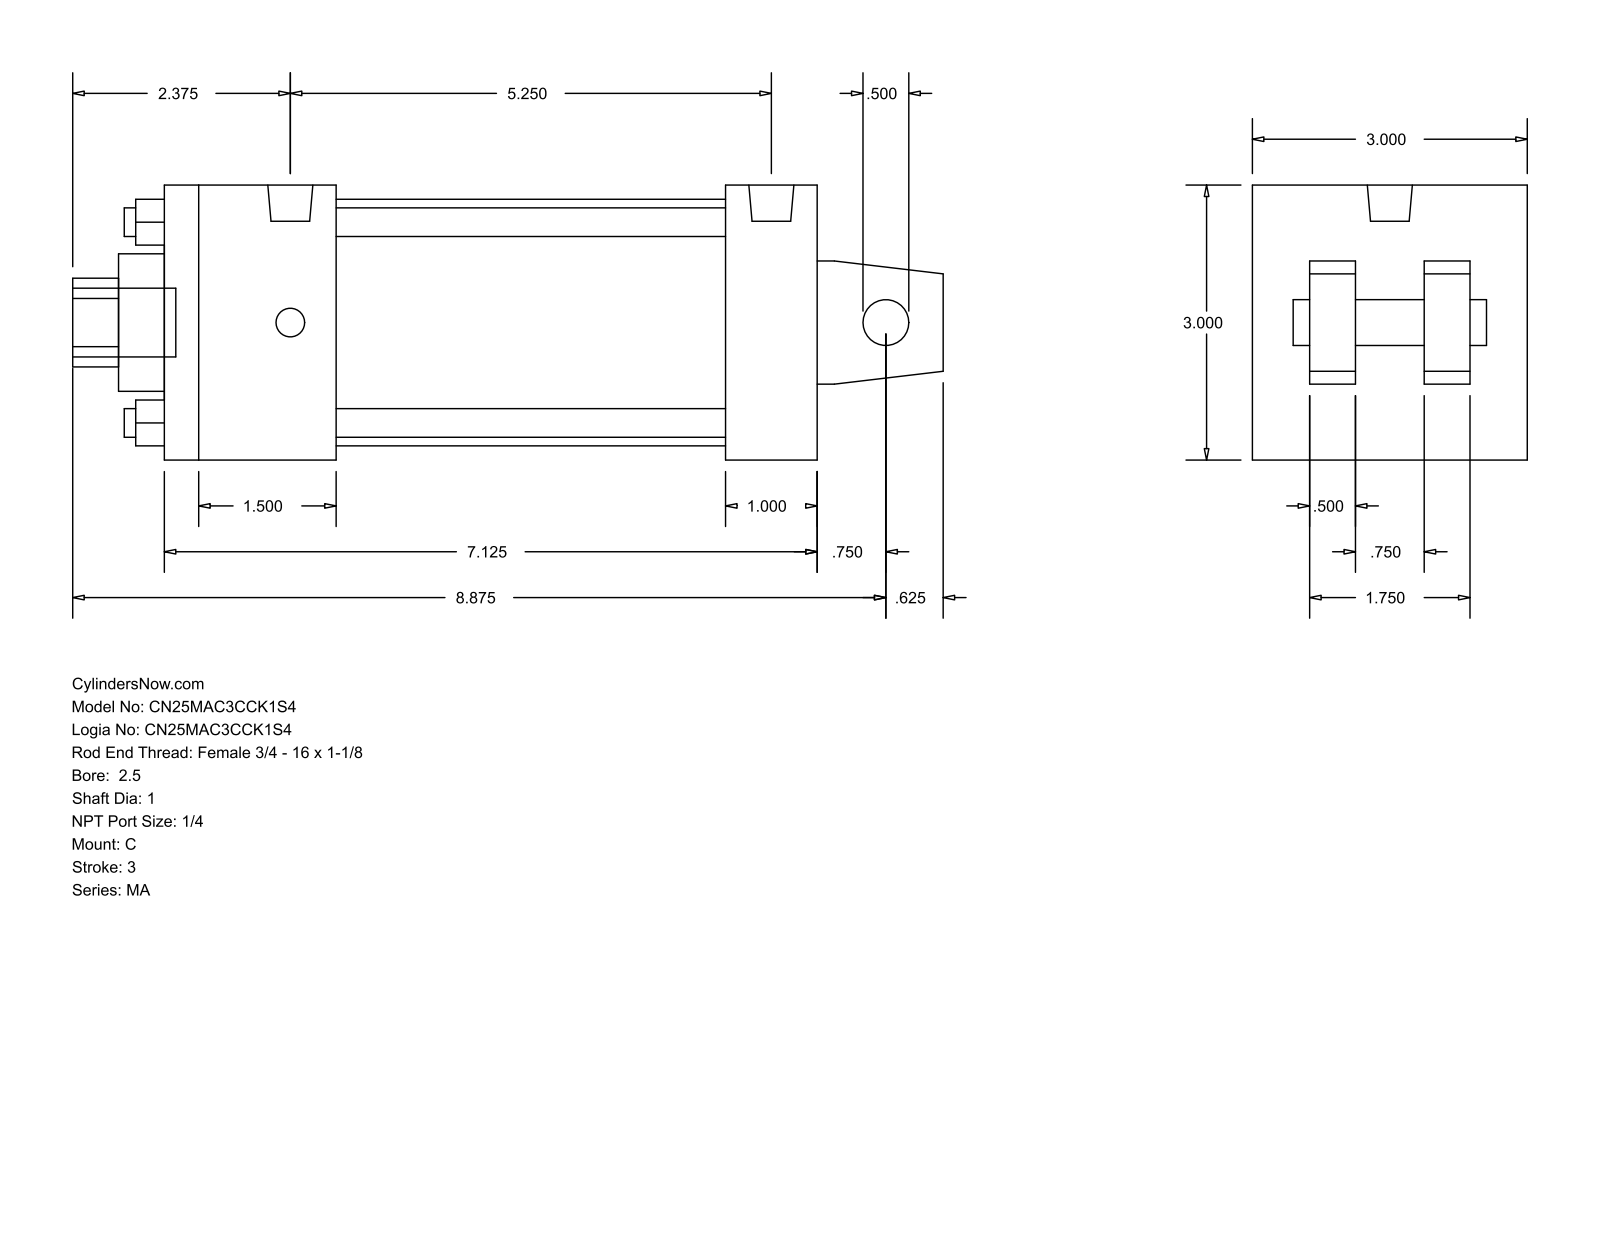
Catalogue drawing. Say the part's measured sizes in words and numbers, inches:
The part is named "MA_C__0250_1". Its 3-D file was written by "GSSL Pune (CONFIG_CONTROL_DESIGN)". It is 0 solids with 103 faces: 76 planar, 27 cylindrical and 0 other. Overall it measures 9.5 by 3 by 3 inches. Round holes: 4 of diameter 0.313, 1 of diameter 0.5, 1 of diameter 1, 1 of diameter 1.5, 1 of diameter 2.69. Round bosses or shafts: 4 of diameter 0.313, 2 of diameter 0.492, 1 of diameter 0.75. Partial cylindrical surfaces (rounded edges, fillets, slot ends): 1 of radius 0.484. The main face-to-face distances are 3, 1.875, 7.125, 0.5, 2.375, 0.625, 1.125, 6.125, 4.25, 5.25. The hole center spacings are 1.548, 2.19, 3.097.
